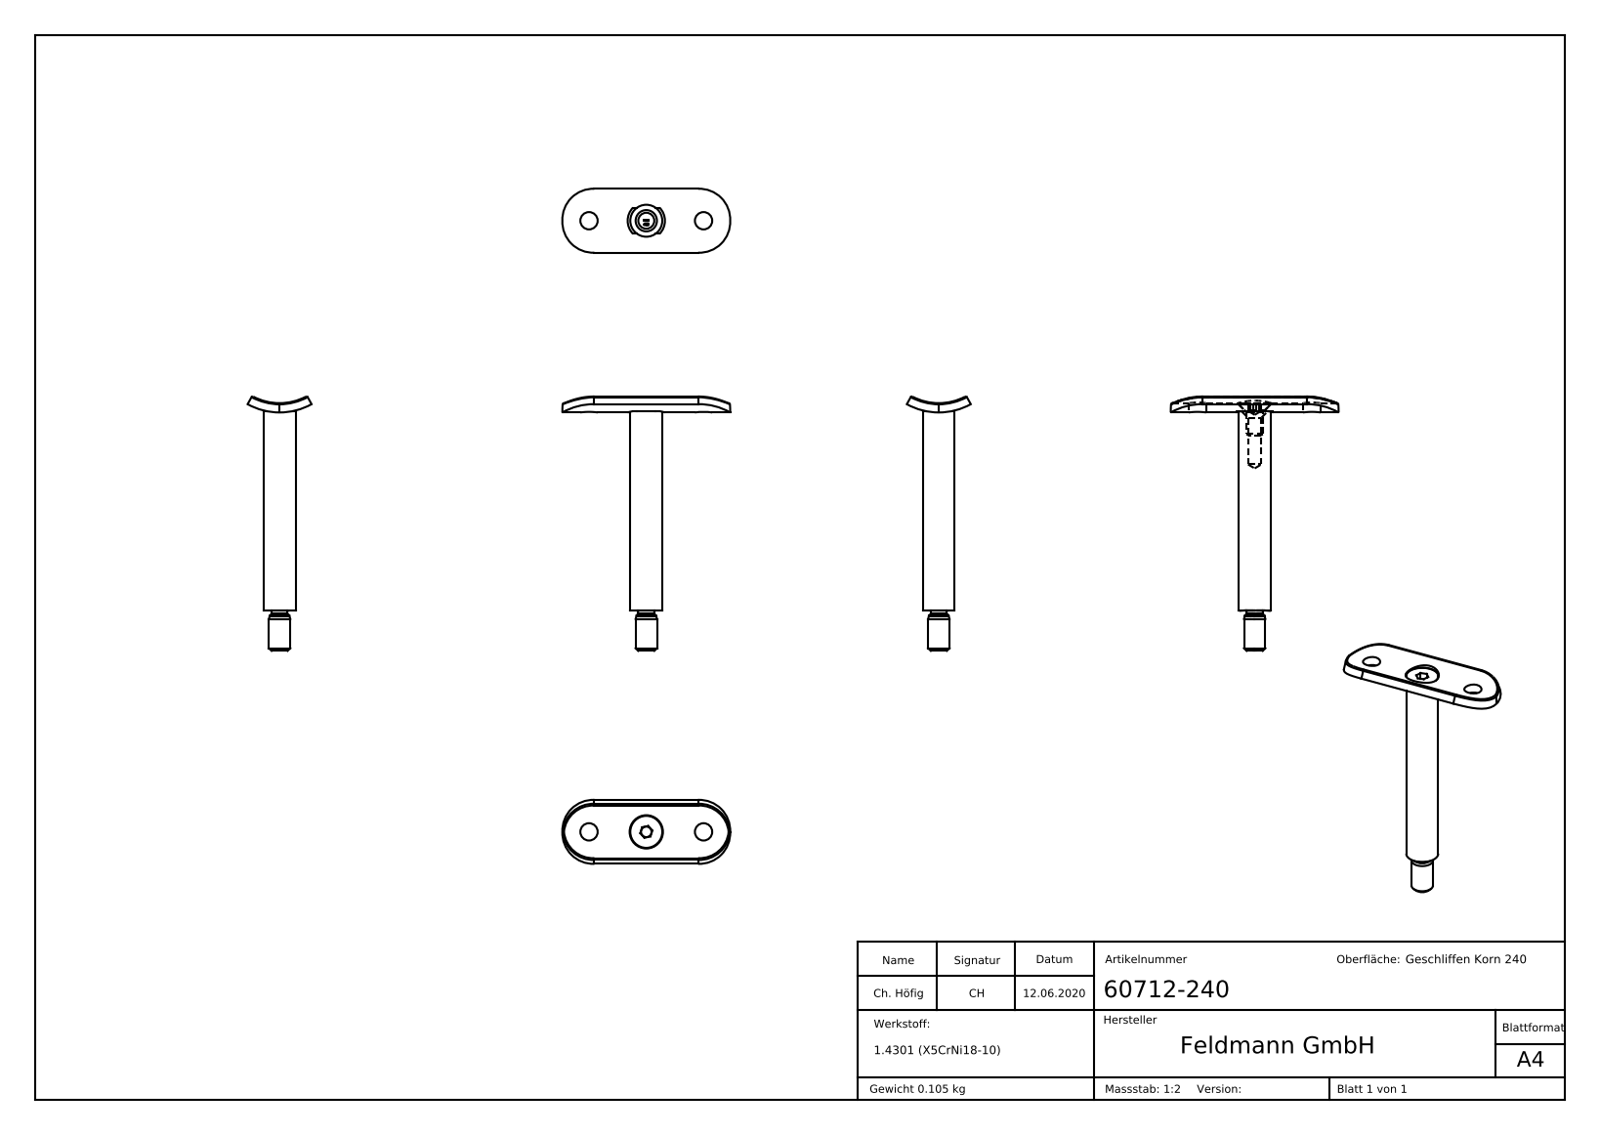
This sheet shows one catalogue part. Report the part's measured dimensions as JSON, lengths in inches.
{"part_name": "60182-240_60182-240; 50236-Konfig_50236-240-75-M6; 60712-240; DIN-7991_-_DIN7991 M6x16 (+3 more)", "step_written_by": "SolidWorks 2015 (CONFIG_CONTROL_DESIGN)", "units": "inches", "bodies": {"solids": 3, "faces": 264, "planar": 136, "cylindrical": 20, "other": 108}, "overall_size": [3.799, 2.48, 0.945], "volume_in3": 0.81, "surface_area_in2": 11.45, "round_holes": [[0.256, 2], [0.197, 1], [0.315, 1], [0.492, 1]], "round_bosses_or_shafts": [[0.472, 1], [0.236, 1]], "partial_cylinders_radius": [[0.472, 4], [0.02, 2], [0.276, 1], [0.835, 1], [0.972, 1]], "face_to_face_distances": [0.11, 3.543, 3.654, 0.157, 3.181, 0.362, 0.472, 3.535, 0.354, 0.118], "hole_center_spacings": [0.846, 1.693]}
